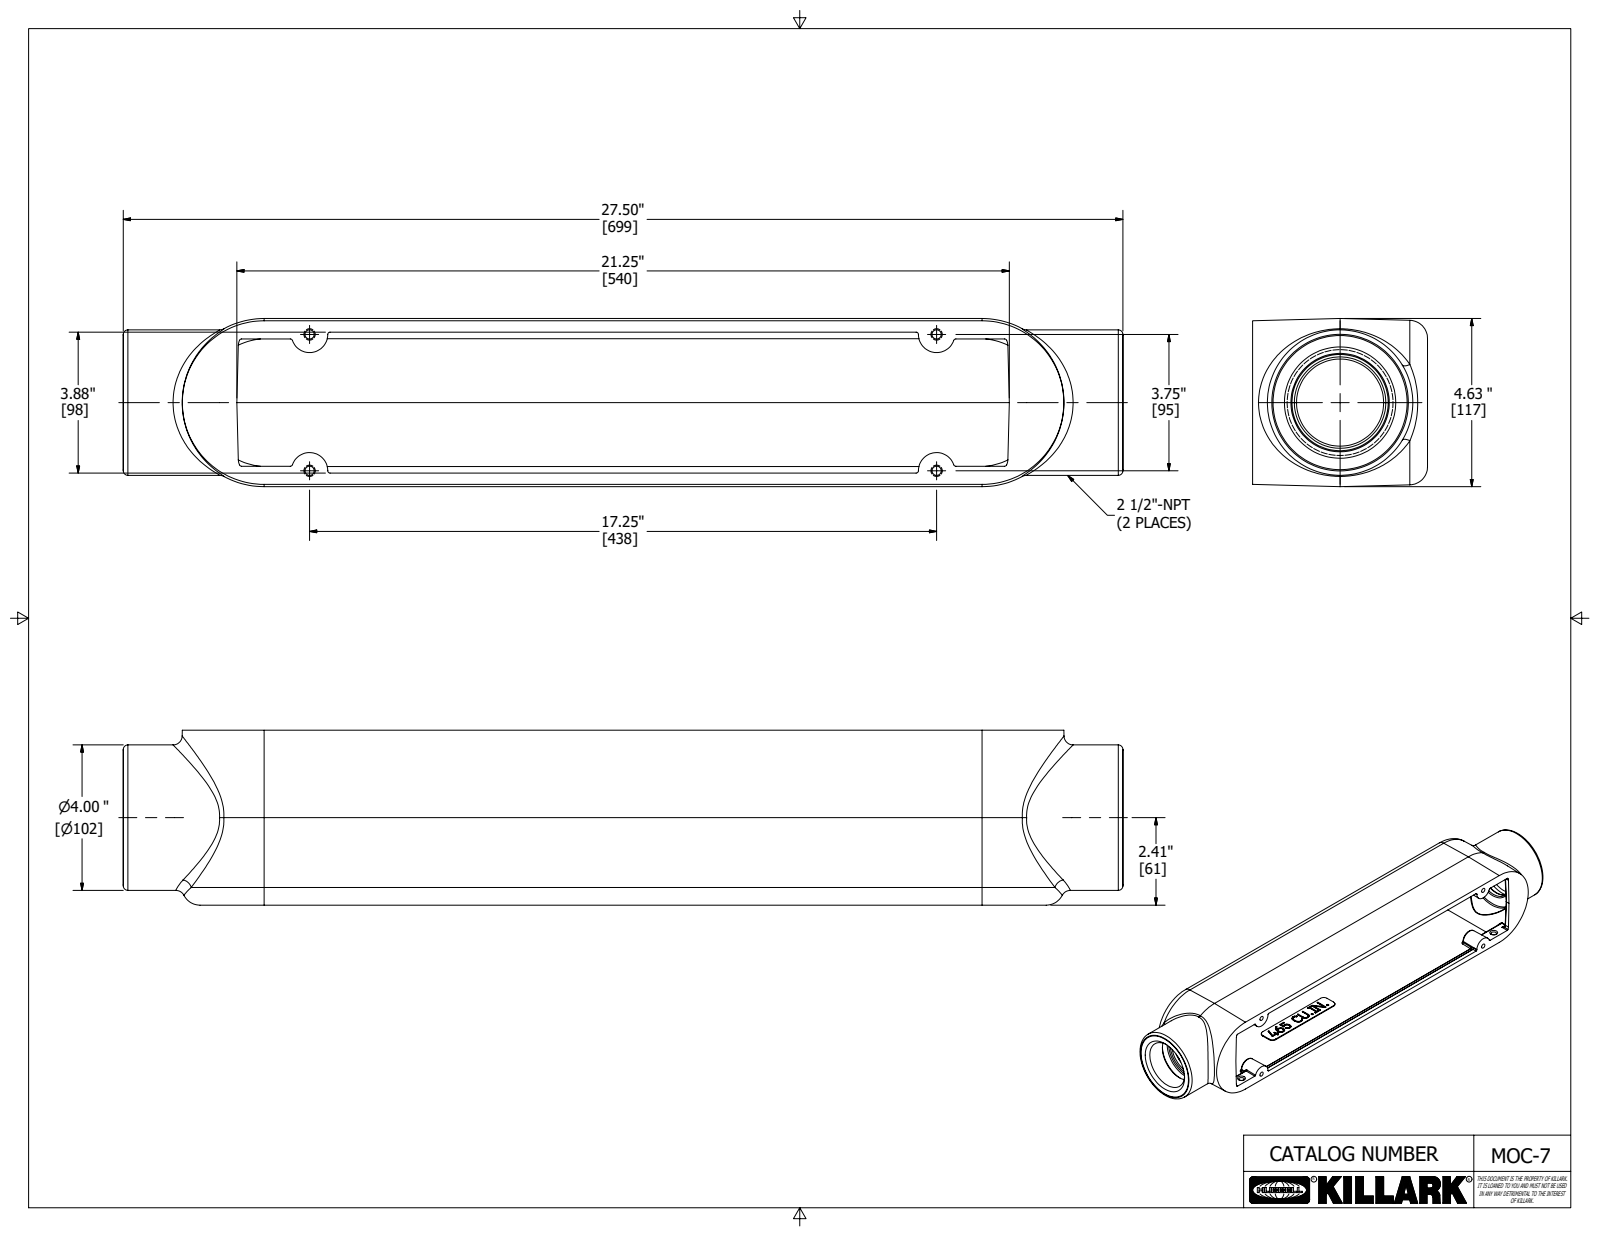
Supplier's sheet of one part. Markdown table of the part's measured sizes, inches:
| quantity | value |
| --- | --- |
| part name | 21243-2 |
| STEP written by | Autodesk Inventor 2020 (AUTOMOTIVE_DESIGN) |
| units | inches |
| bodies | 1 solid, 670 faces (274 planar, 92 cylindrical, 304 other) |
| overall size | 27.5 × 4.813 × 4.625 |
| volume | 126.7 in³ |
| surface area | 781.3 in² |
| round holes (diameter × count) | 0.252 × 4, 2.396 × 1, 2.886 × 1 |
| round bosses / shafts (diameter × count) | 4 × 1, 3.688 × 1 |
| partial cylindrical surfaces (radius × count) | 0.062 × 50, 0.375 × 4, 0.125 × 2, 0.249 × 2, 0.5 × 2, 2 × 2 |
| main face-to-face distances | 4.625, 4, 4.813, 0.031, 4.781, 0.063, 3.937, 23.601, 4.25, 0.031 |
| hole center spacings | 3.75, 17.25, 17.652 |
